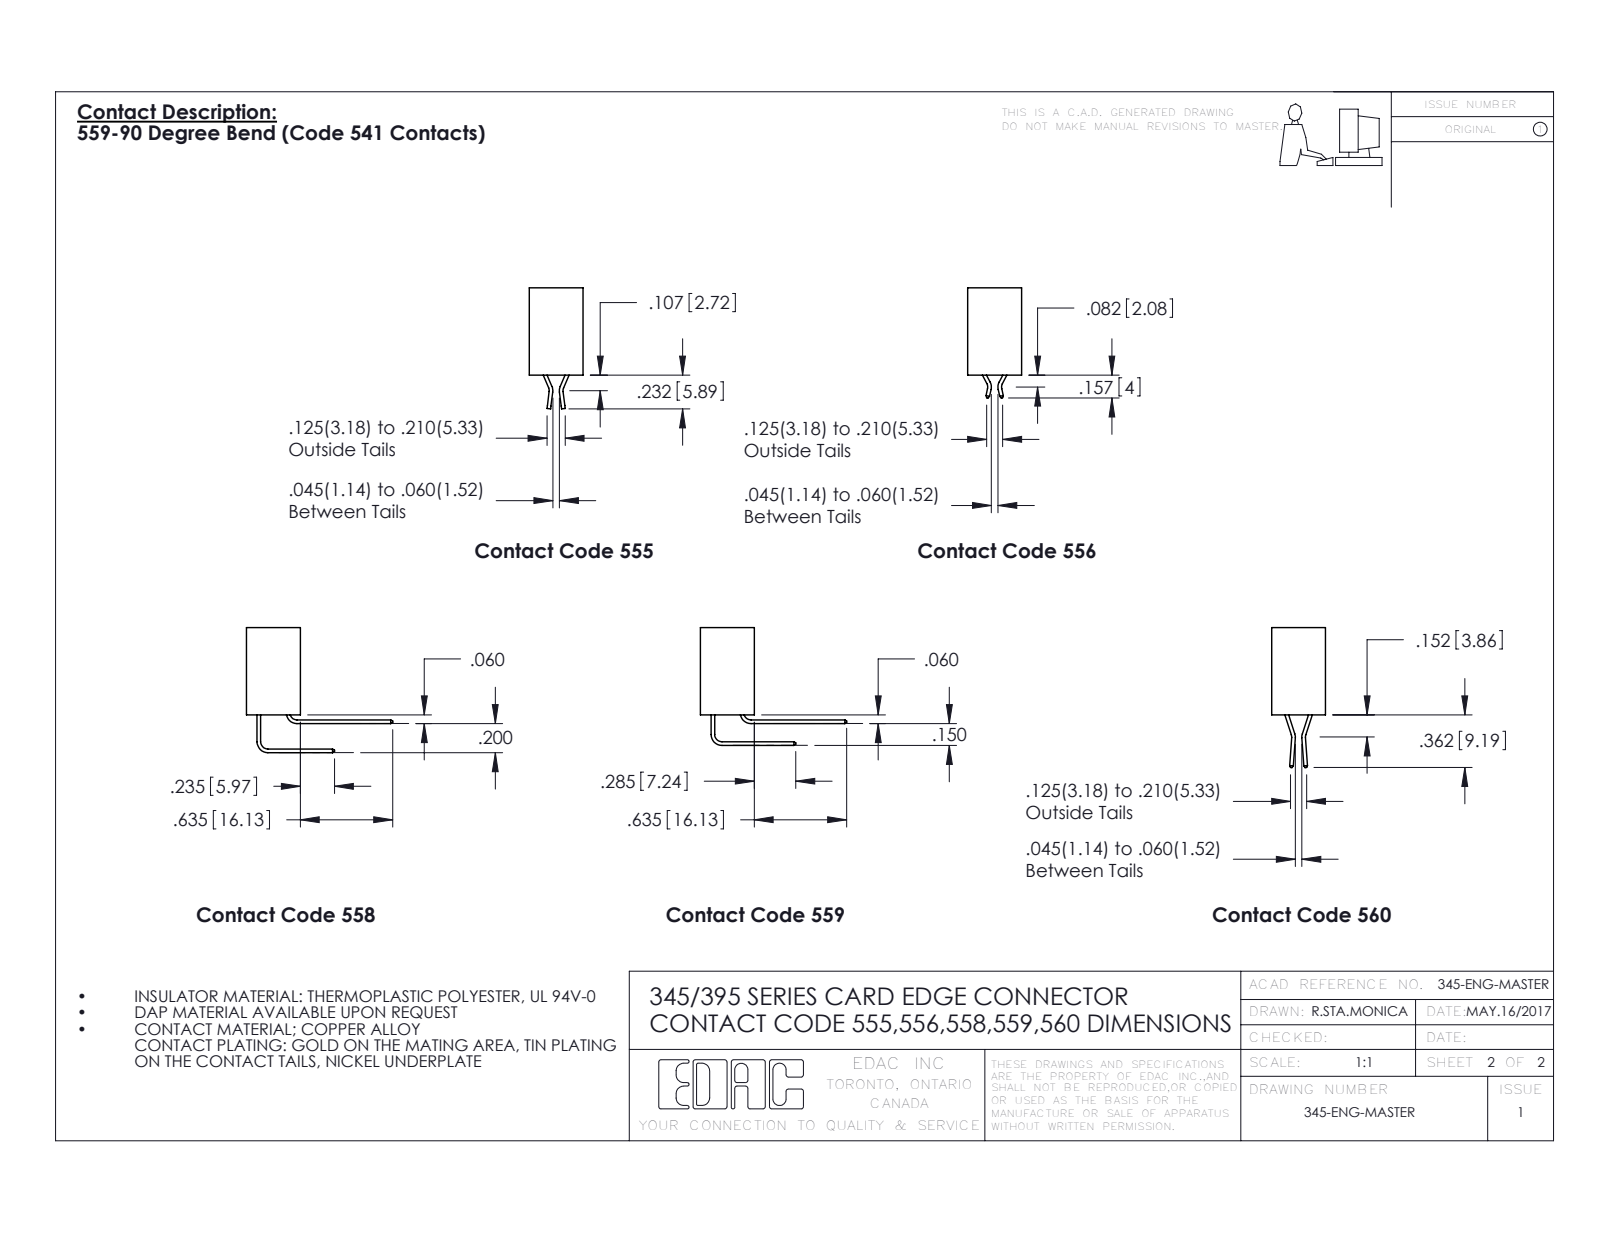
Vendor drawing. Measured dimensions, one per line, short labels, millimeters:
name: 345 Part_No Mounting Lugs; 345-292-001_345-293-124; 395-032-524-101
written by: SolidWorks 2016 (CONFIG_CONTROL_DESIGN)
unit: mm
bodies: 33 solids, 2102 faces (1548 planar, 554 cylindrical, 0 other)
size: 87.9 × 19.4 × 9.4
volume: 8 720 mm³; area: 11 250 mm²
holes: 1× ⌀1.6
rounds: 64× R0.2, 22× R0.3, 6× R0.2, 6× R0.8, 3× R0.7, 2× R0.8, 2× R1, 1× R0.4
face distances: 7.6, 1.8, 9.4, 5.1, 2.5, 6.9, 0.6, 5.7, 1.8, 3.8
